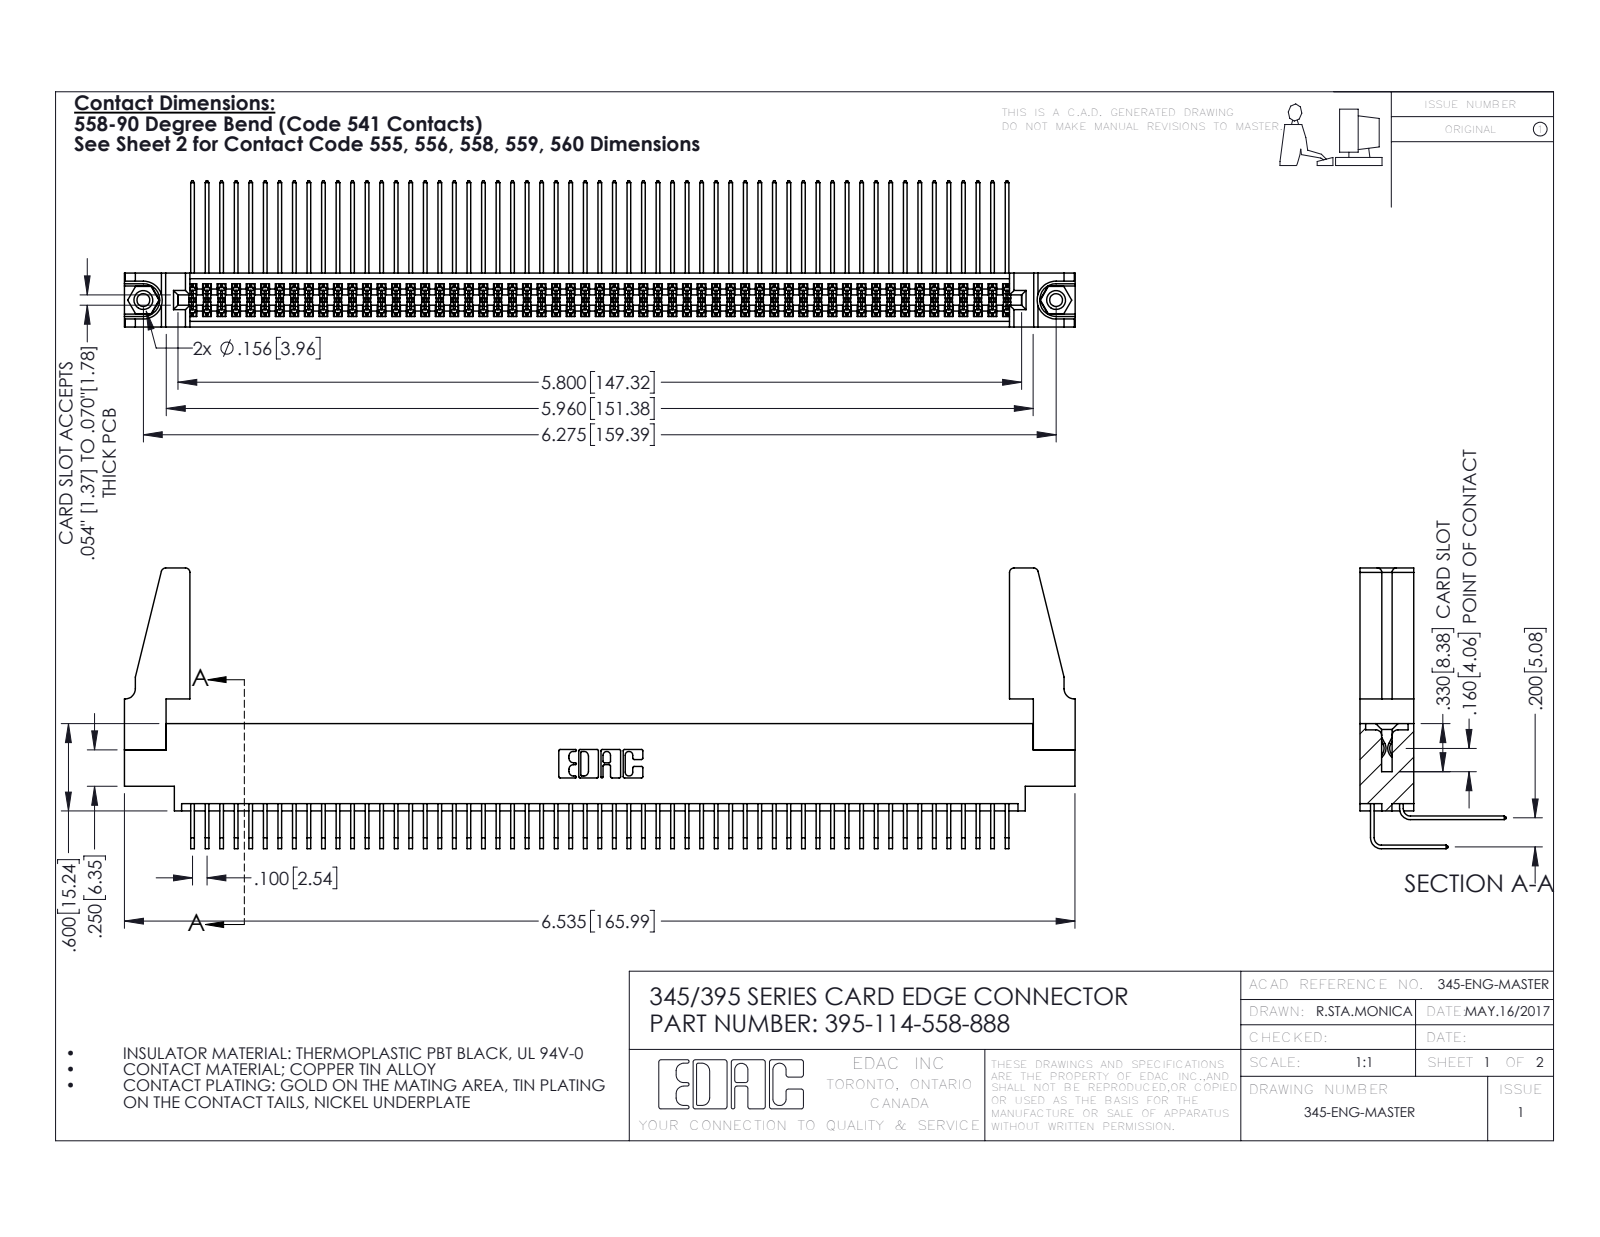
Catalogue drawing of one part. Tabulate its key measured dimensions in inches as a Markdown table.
| quantity | value |
| --- | --- |
| part name | 395-114-558-888; 345-292-001_558 Tail - 2; 345-250-001_345-250-001-102; 345 Part_0.170 Offset - 0.156 Dia-TH (+2 more) |
| STEP written by | SolidWorks 2016 (CONFIG_CONTROL_DESIGN) |
| units | inches |
| bodies | 119 solids, 6182 faces (4146 planar, 2020 cylindrical, 16 other) |
| overall size | 6.536 × 1.929 × 1.005 |
| volume | 1.224 in³ |
| surface area | 48.82 in² |
| round holes (diameter × count) | 0.089 × 2, 0.125 × 2, 0.156 × 2, 0.064 × 1 |
| round bosses / shafts (diameter × count) | 0.155 × 2 |
| partial cylindrical surfaces (radius × count) | 0.006 × 172, 0.01 × 22, 0.03 × 8, 0.007 × 6, 0.031 × 6, 0.026 × 3, 0.014 × 2, 0.019 × 2 |
| main face-to-face distances | 0.072, 0.298, 0.2, 0.37, 0.098, 0.272, 0.025, 0.225, 0.175, 0.025 |
| hole center spacings | 0.27, 6.039, 6.275 |
